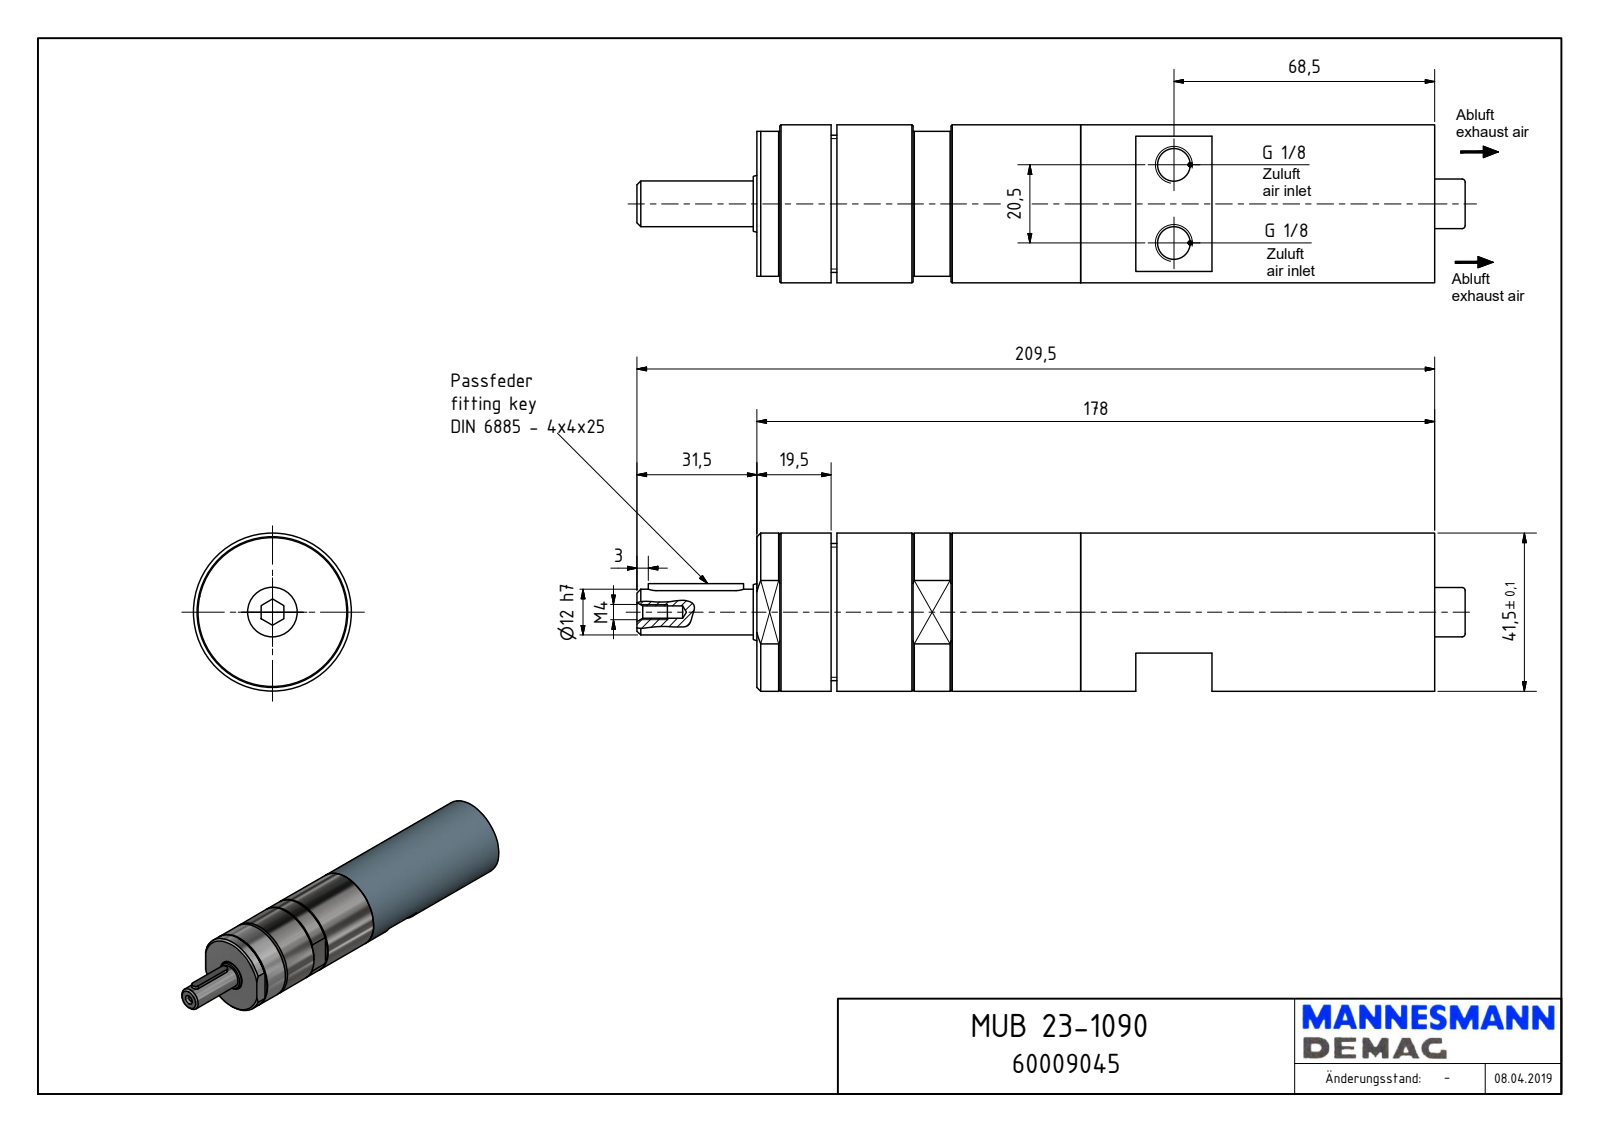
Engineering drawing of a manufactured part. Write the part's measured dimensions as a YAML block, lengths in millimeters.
part_name: "MUB 23-1090_60009045"
step_written_by: "Autodesk Inventor 2018 (AUTOMOTIVE_DESIGN)"
units: millimeters
bodies: {solids: 1, faces: 116, planar: 53, cylindrical: 42, other: 21}
overall_size: [217.5, 41.5, 41.5]
volume: 237464
surface_area: 32478
round_holes:
  - {diameter: 8.57, count: 2}
  - {diameter: 3.24, count: 1}
  - {diameter: 13, count: 1}
  - {diameter: 16, count: 1}
  - {diameter: 37, count: 1}
  - {diameter: 39.5, count: 1}
round_bosses_or_shafts:
  - {diameter: 41.5, count: 1}
  - {diameter: 39.39, count: 1}
  - {diameter: 39, count: 1}
  - {diameter: 36, count: 1}
  - {diameter: 14.95, count: 1}
  - {diameter: 12, count: 1}
partial_cylinders:
  - {radius: 2, count: 4}
  - {radius: 1, count: 2}
  - {radius: 2.5, count: 2}
  - {radius: 8.1, count: 1}
  - {radius: 12.99, count: 1}
face_to_face_distances: [178, 123.02, 54.98, 78.5, 55, 123, 21, 1.5, 19.5, 103.5]
hole_center_spacings: [20.5]
